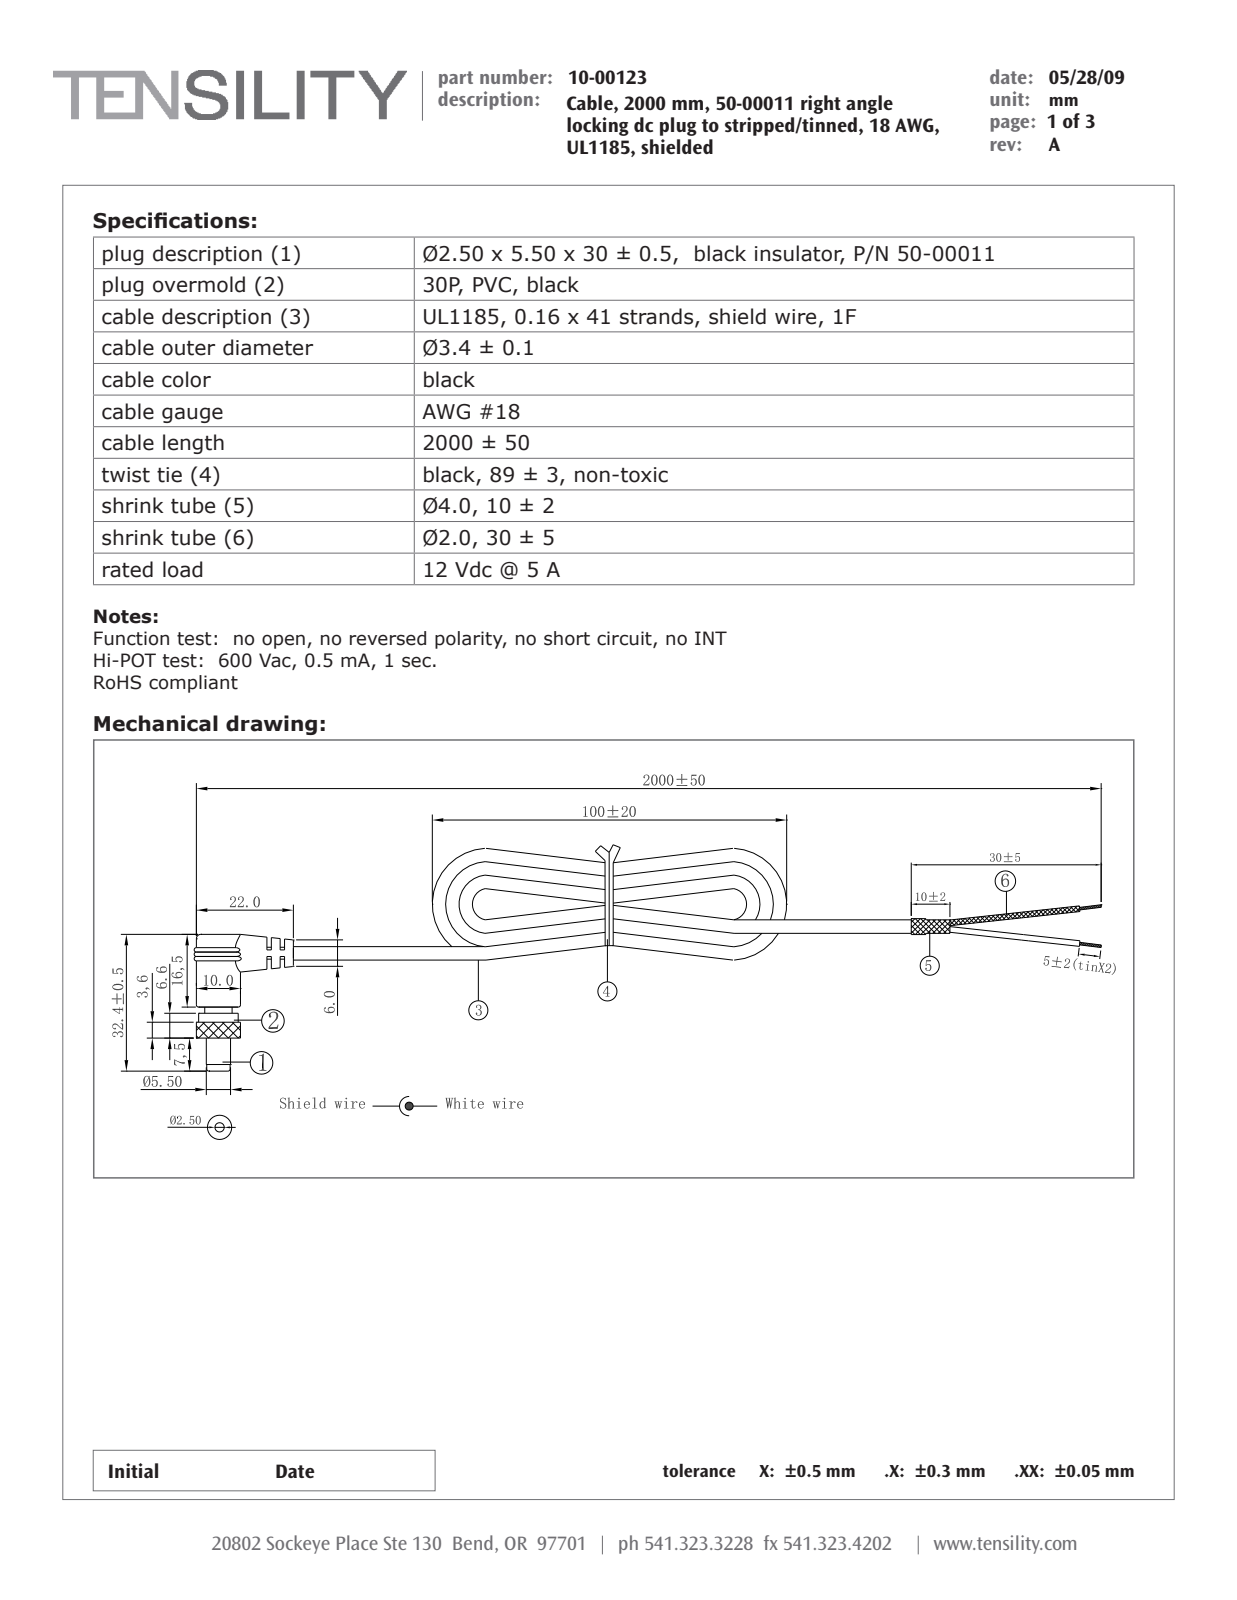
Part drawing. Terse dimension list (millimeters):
name: 24-00017; 10-00123; 50-00011; 30-00004_stripped and tinned (+6 more)
written by: SolidWorks 2015 (CONFIG_CONTROL_DESIGN)
unit: mm
bodies: 176 solids, 1963 faces (673 planar, 562 cylindrical, 728 other)
size: 191.5 × 34 × 11
volume: 3 867 mm³; area: 15 134 mm²
holes: 1× ⌀1.26, 1× ⌀1.6, 1× ⌀2.16, 1× ⌀2.4, 1× ⌀2.5, 1× ⌀3, 1× ⌀3.25, 1× ⌀4.25, 1× ⌀5.04, 1× ⌀5.44, 1× ⌀5.5, 1× ⌀5.65
bosses: 1× ⌀11, 1× ⌀10, 1× ⌀8.5, 1× ⌀7, 1× ⌀6.2, 1× ⌀6, 1× ⌀5.48, 1× ⌀5.3
rounds: 4× R0.55
face distances: 1, 3, 10, 5, 2, 16.5, 13.4, 7.5, 9, 26.5
